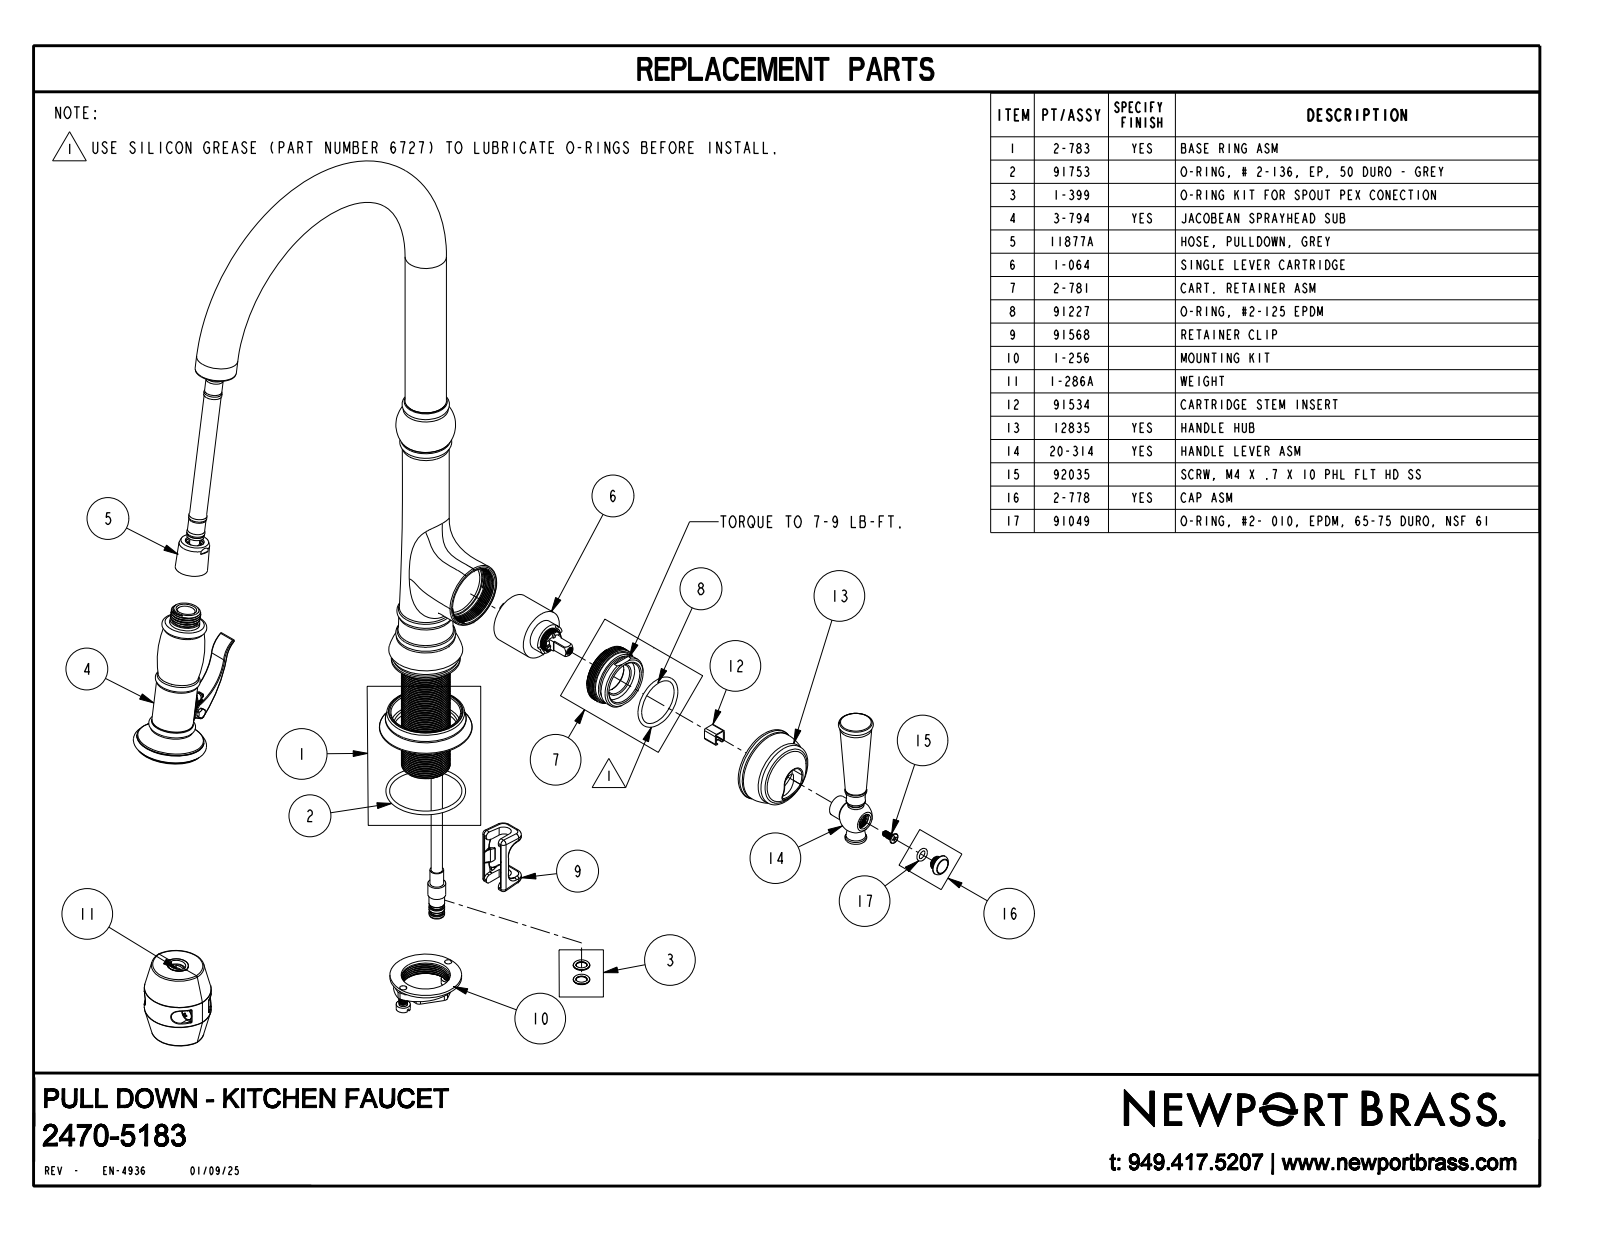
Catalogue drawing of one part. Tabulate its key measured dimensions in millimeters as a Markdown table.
| quantity | value |
| --- | --- |
| part name | 2470-5173 |
| STEP written by | CREO PARAMETRIC BY PTC INC, 2023134 (CONFIG_CONTROL_DESIGN) |
| units | millimeters |
| bodies | 1 solid, 1372 faces (892 planar, 197 cylindrical, 283 other) |
| overall size | 468.2 × 279.9 × 124.7 |
| volume | 748 900 mm³ |
| surface area | 104 100 mm² |
| round holes (diameter × count) | 1 × 18, 5.3 × 1, 12 × 1, 14.2 × 1, 26.3 × 1 |
| round bosses / shafts (diameter × count) | 2.6 × 18, 51.3 × 1, 47.1 × 1, 29.3 × 1, 29 × 1, 27.7 × 1, 23.8 × 1, 15.1 × 1 |
| partial cylindrical surfaces (radius × count) | 0.8 × 21, 0.5 × 16, 1.7 × 14, 0.6 × 7, 1.5 × 5, 1.1 × 4, 1 × 1, 2.5 × 1 |
| main face-to-face distances | 18.9, 47.2, 66.1, 12.7, 34.5, 53.4, 0.8, 17.1, 0.9, 100.6 |
| hole center spacings | 9.3, 3.3, 18.4, 12, 16.2, 17.6, 6.4, 6.4 |
